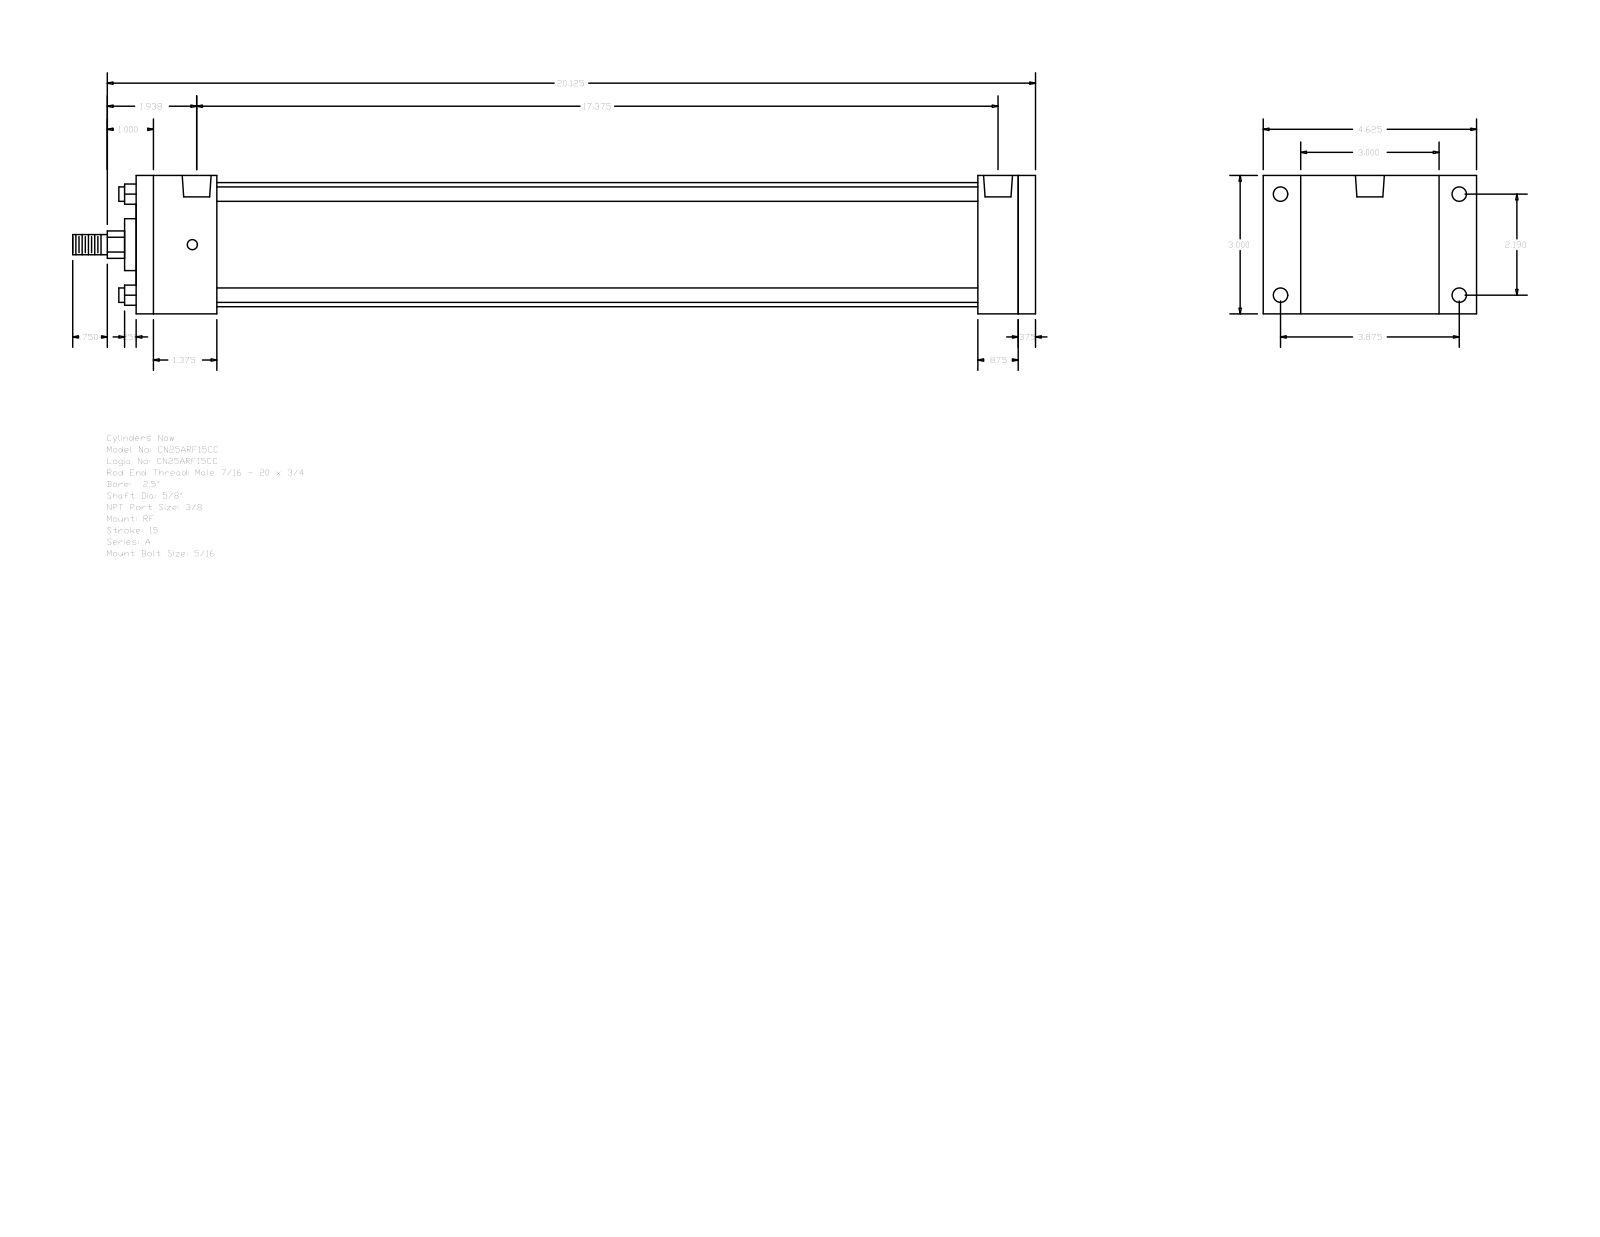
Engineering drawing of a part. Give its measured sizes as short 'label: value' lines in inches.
name: A_RF__0250_0.625
written by: GSSL Pune (CONFIG_CONTROL_DESIGN)
unit: in
bodies: 0 solids, 92 faces (64 planar, 28 cylindrical, 0 other)
size: 20.875 × 4.625 × 3
holes: 4× ⌀0.219, 4× ⌀0.313, 2× ⌀0.627
bosses: 4× ⌀0.313, 1× ⌀2.69, 1× ⌀1.125, 1× ⌀0.625, 1× ⌀0.437
rounds: 1× R0.297
face distances: 3, 19.5, 0.375, 19.125, 1.75, 1.25, 18.25, 16.5, 17.375, 17.75
hole spacings: 0.094, 2.19, 3.875, 4.451, 17.469, 17.563, 17.375
